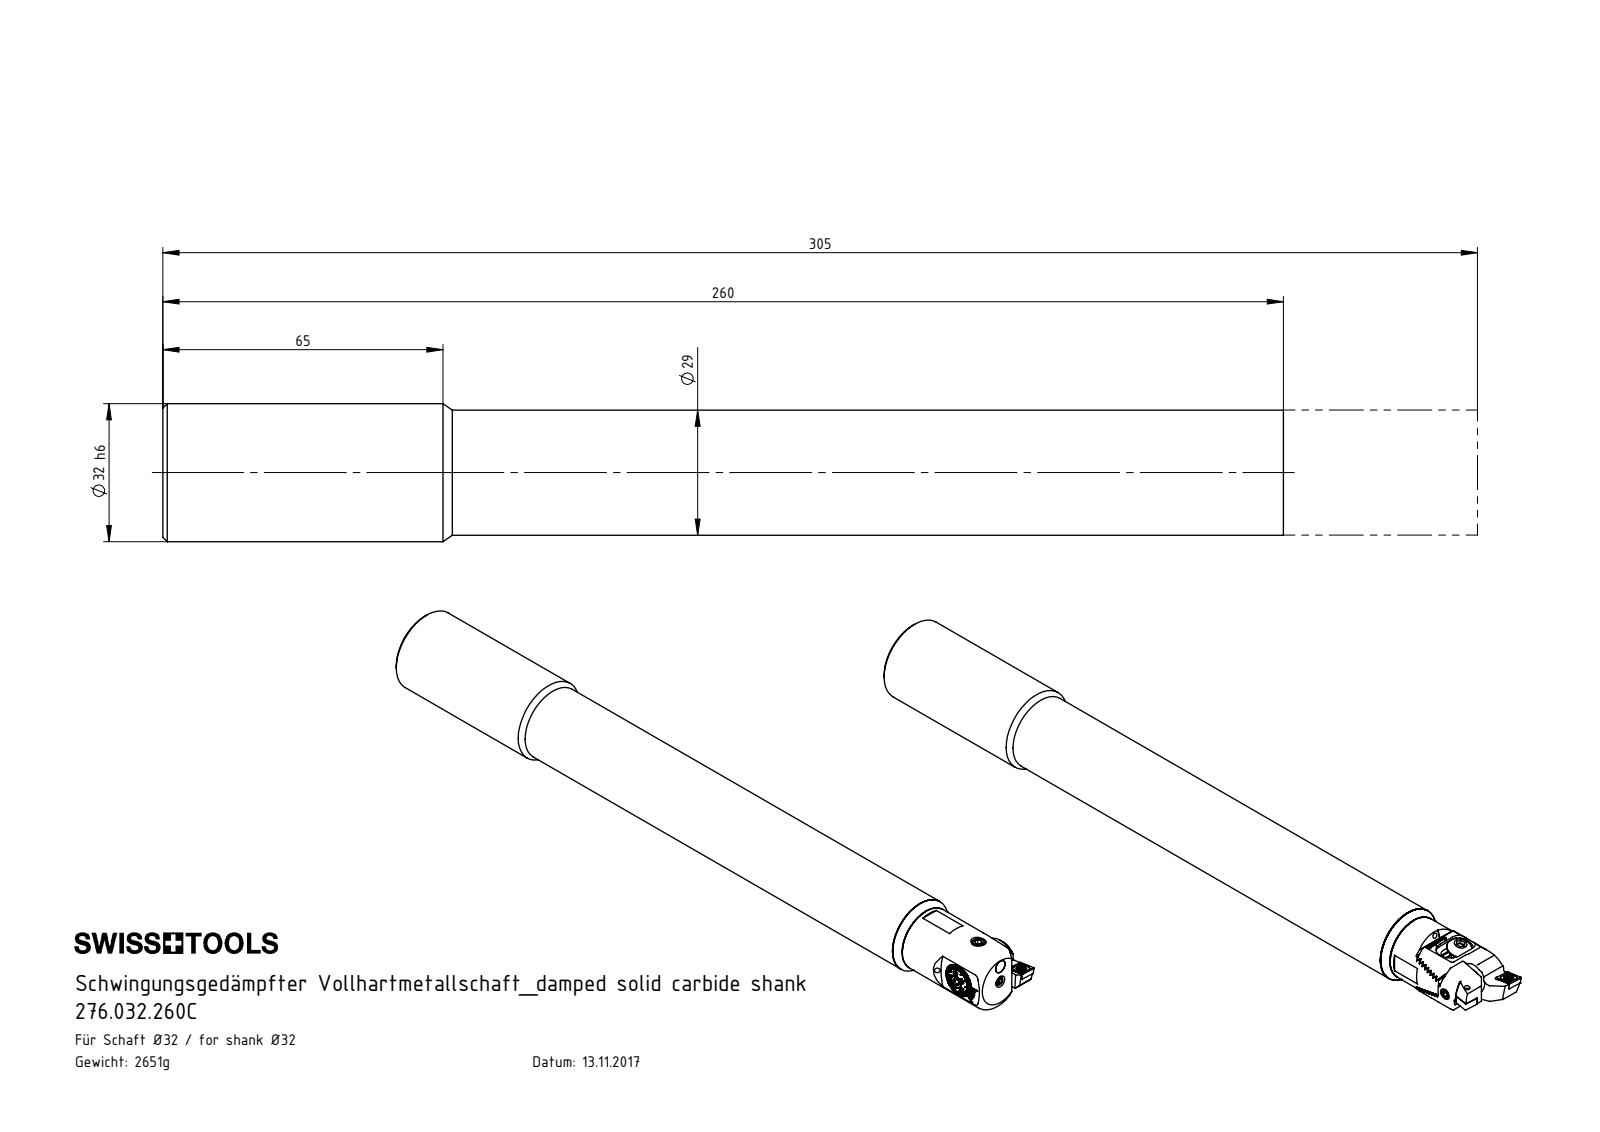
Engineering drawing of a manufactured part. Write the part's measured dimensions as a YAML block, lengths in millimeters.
part_name: "F25-WCA.001.006; ISO 4026 - M5 x 4_PreviewCfg; WCA-ER2.001.006_A; T7 M2.5 x 6_PreviewCfg (+8 more)"
step_written_by: "SolidWorks 2017 (CONFIG_CONTROL_DESIGN)"
units: millimeters
bodies: {solids: 22, faces: 878, planar: 372, cylindrical: 172, other: 334}
overall_size: [305, 32, 32]
volume: 195471
surface_area: 49652
round_holes:
  - {diameter: 2, count: 5}
  - {diameter: 4.2, count: 3}
  - {diameter: 2.05, count: 2}
  - {diameter: 2.1, count: 1}
  - {diameter: 2.4, count: 1}
  - {diameter: 2.7, count: 1}
  - {diameter: 2.8, count: 1}
  - {diameter: 3, count: 1}
  - {diameter: 3.3, count: 1}
  - {diameter: 3.85, count: 1}
  - {diameter: 5, count: 1}
  - {diameter: 5.5, count: 1}
round_bosses_or_shafts:
  - {diameter: 5, count: 2}
  - {diameter: 4.95, count: 2}
  - {diameter: 2.5, count: 2}
  - {diameter: 32, count: 1}
  - {diameter: 29, count: 1}
  - {diameter: 25, count: 1}
  - {diameter: 16, count: 1}
  - {diameter: 12.98, count: 1}
partial_cylinders:
  - {radius: 0.21, count: 6}
  - {radius: 0.36, count: 5}
  - {radius: 0.5, count: 4}
  - {radius: 1.32, count: 2}
  - {radius: 0.2, count: 1}
  - {radius: 0.36, count: 1}
  - {radius: 1.05, count: 1}
  - {radius: 1.25, count: 1}
face_to_face_distances: [260, 3, 224, 36, 263, 39, 302.15, 78.15, 42.15, 39.15]
hole_center_spacings: [3.84, 3.99, 4.48, 6.8, 9.46, 16.65]
